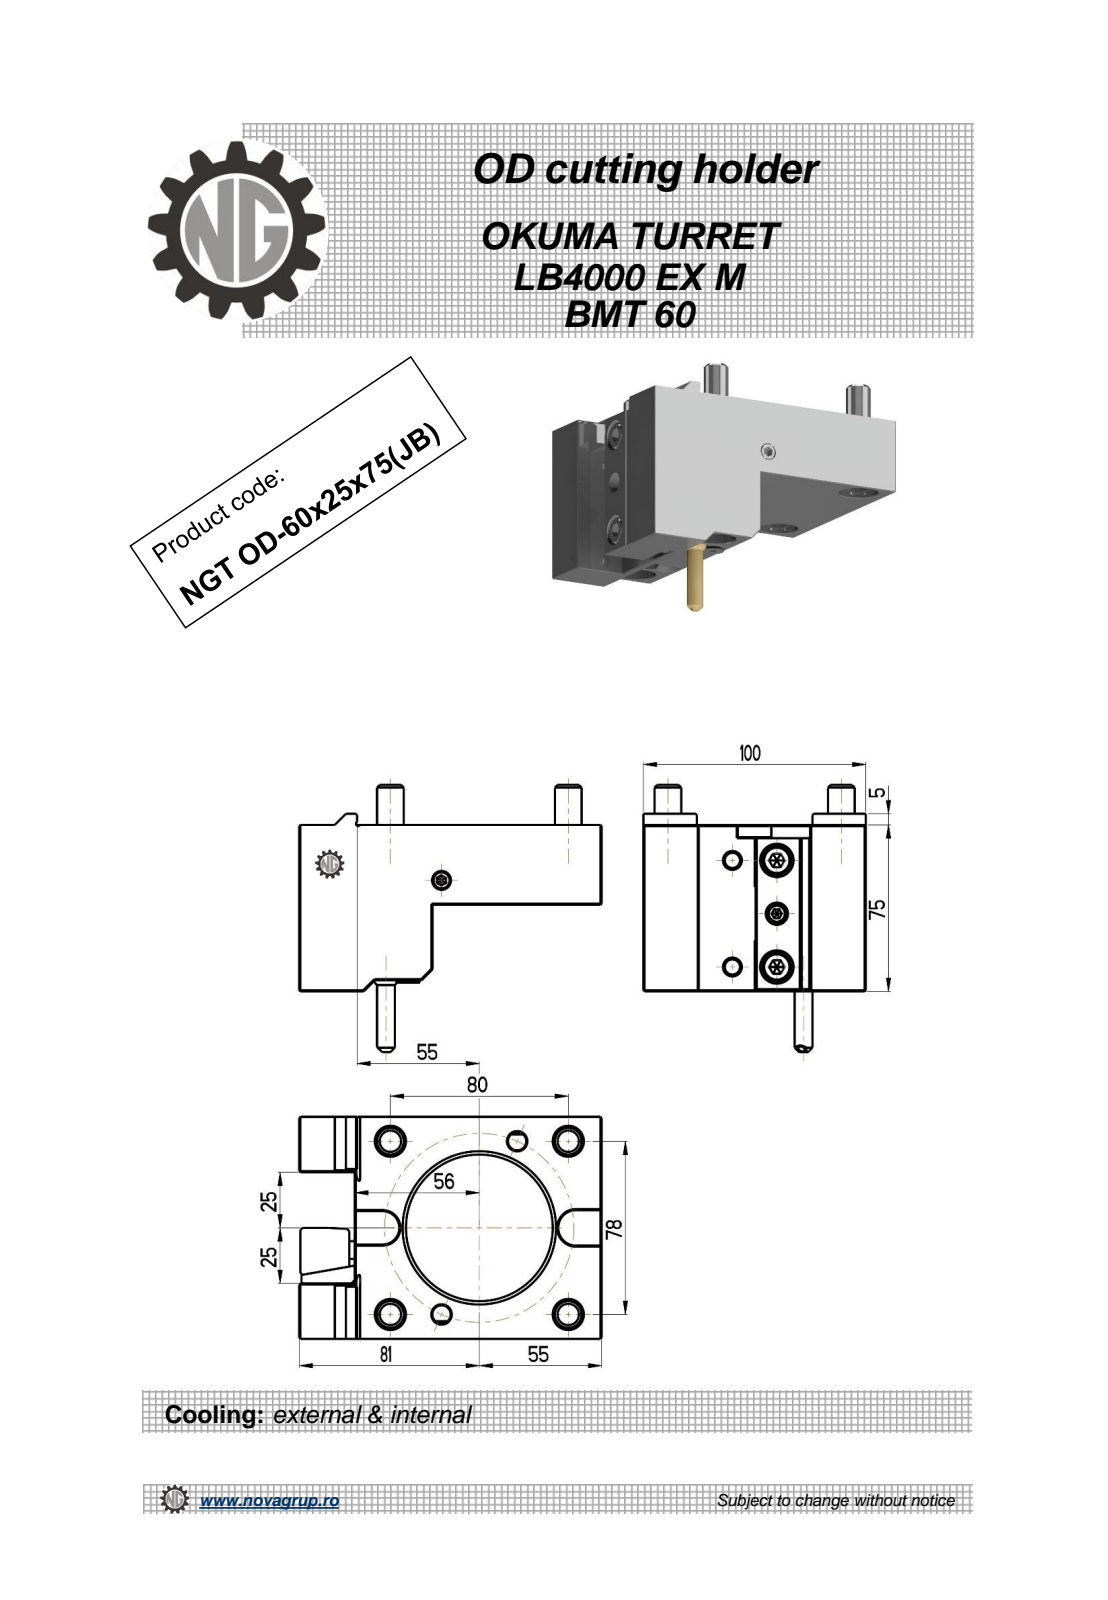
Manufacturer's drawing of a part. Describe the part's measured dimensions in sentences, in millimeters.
The part is named "NGT_OD_60_25_75_JB". Its 3-D file was written by "PRO/ENGINEER BY PARAMETRIC TECHNOLOGY CORPORATION, 2010280 (CONFIG_CONTROL_DESIGN)". It is 1 solid with 202 faces: 121 planar, 45 cylindrical and 36 other. Overall it measures 136 by 120.34 by 100 millimeters. Its volume is 656 611 cubic millimeters and its surface area 68 712 square millimeters. Round holes: 2 of diameter 8.2, 1 of diameter 3, 1 of diameter 5, 1 of diameter 69. Round bosses or shafts: 4 of diameter 12, 4 of diameter 8, 1 of diameter 61, 1 of diameter 11.2. Partial cylindrical surfaces (rounded edges, fillets, slot ends): 6 of radius 0.22, 2 of radius 0.4, 2 of radius 4, 1 of radius 1, 1 of radius 7.5, 1 of radius 8. The main face-to-face distances are 36, 100, 25, 75, 136, 76, 111, 35, 60, 34. The hole center spacings are 42.54, 30.23, 47.41, 84.86, 85.09.
